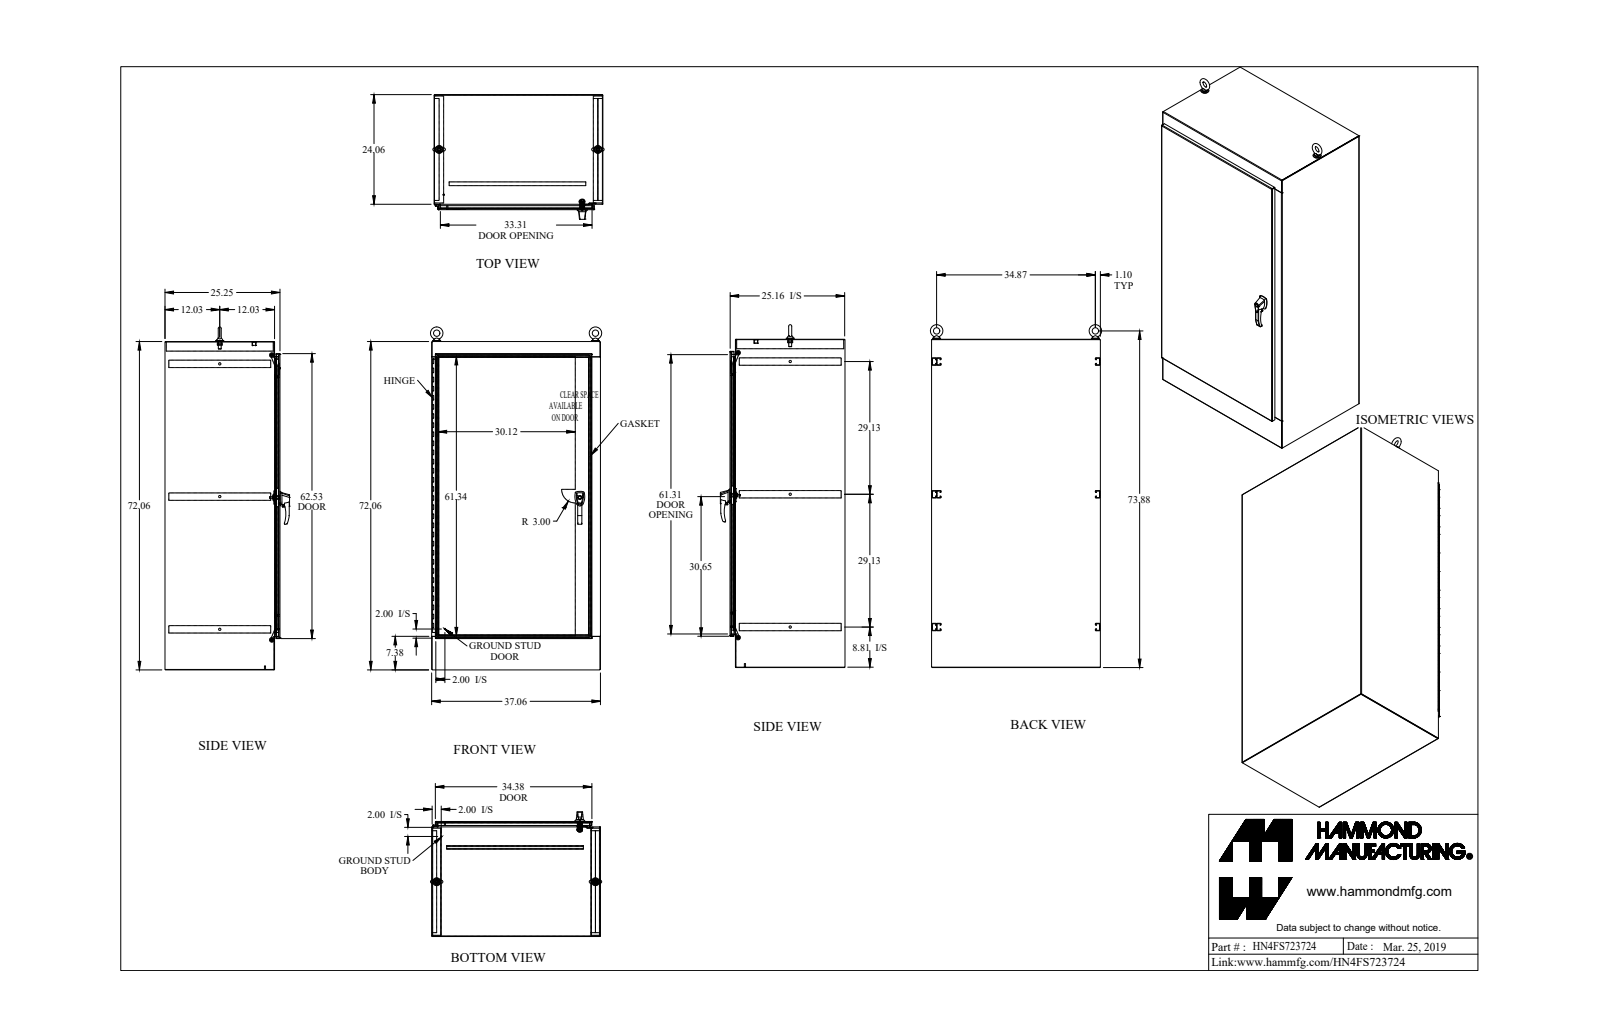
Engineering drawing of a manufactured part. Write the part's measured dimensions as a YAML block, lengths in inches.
part_name: "HN4FS723724"
step_written_by: "SolidWorks 2018 (AUTOMOTIVE_DESIGN)"
units: inches
bodies: {solids: 56, faces: 1971, planar: 921, cylindrical: 885, other: 165}
overall_size: [75.483, 37.604, 27.362]
volume: 1225
surface_area: 25758
round_holes:
  - {diameter: 0.304, count: 10}
  - {diameter: 0.35, count: 7}
  - {diameter: 0.5, count: 3}
  - {diameter: 0.25, count: 2}
  - {diameter: 0.257, count: 2}
  - {diameter: 0.28, count: 2}
  - {diameter: 0.281, count: 2}
  - {diameter: 0.313, count: 2}
  - {diameter: 0.39, count: 2}
  - {diameter: 0.413, count: 2}
  - {diameter: 0.527, count: 2}
  - {diameter: 0.687, count: 2}
round_bosses_or_shafts:
  - {diameter: 0.281, count: 4}
  - {diameter: 1.75, count: 2}
  - {diameter: 1.5, count: 2}
  - {diameter: 1.25, count: 2}
  - {diameter: 1, count: 2}
  - {diameter: 0.75, count: 2}
  - {diameter: 0.738, count: 2}
  - {diameter: 0.63, count: 2}
partial_cylinders:
  - {radius: 0.043, count: 60}
  - {radius: 0.138, count: 54}
  - {radius: 0.5, count: 23}
  - {radius: 0.125, count: 22}
  - {radius: 0.018, count: 16}
  - {radius: 0.048, count: 15}
  - {radius: 0.06, count: 15}
  - {radius: 0.143, count: 15}
face_to_face_distances: [0.095, 25.152, 36.965, 25.057, 25.247, 36.87, 71.965, 37.06, 23.965, 1.187]
hole_center_spacings: [6, 12, 18, 24, 30, 36, 42, 0.015]
